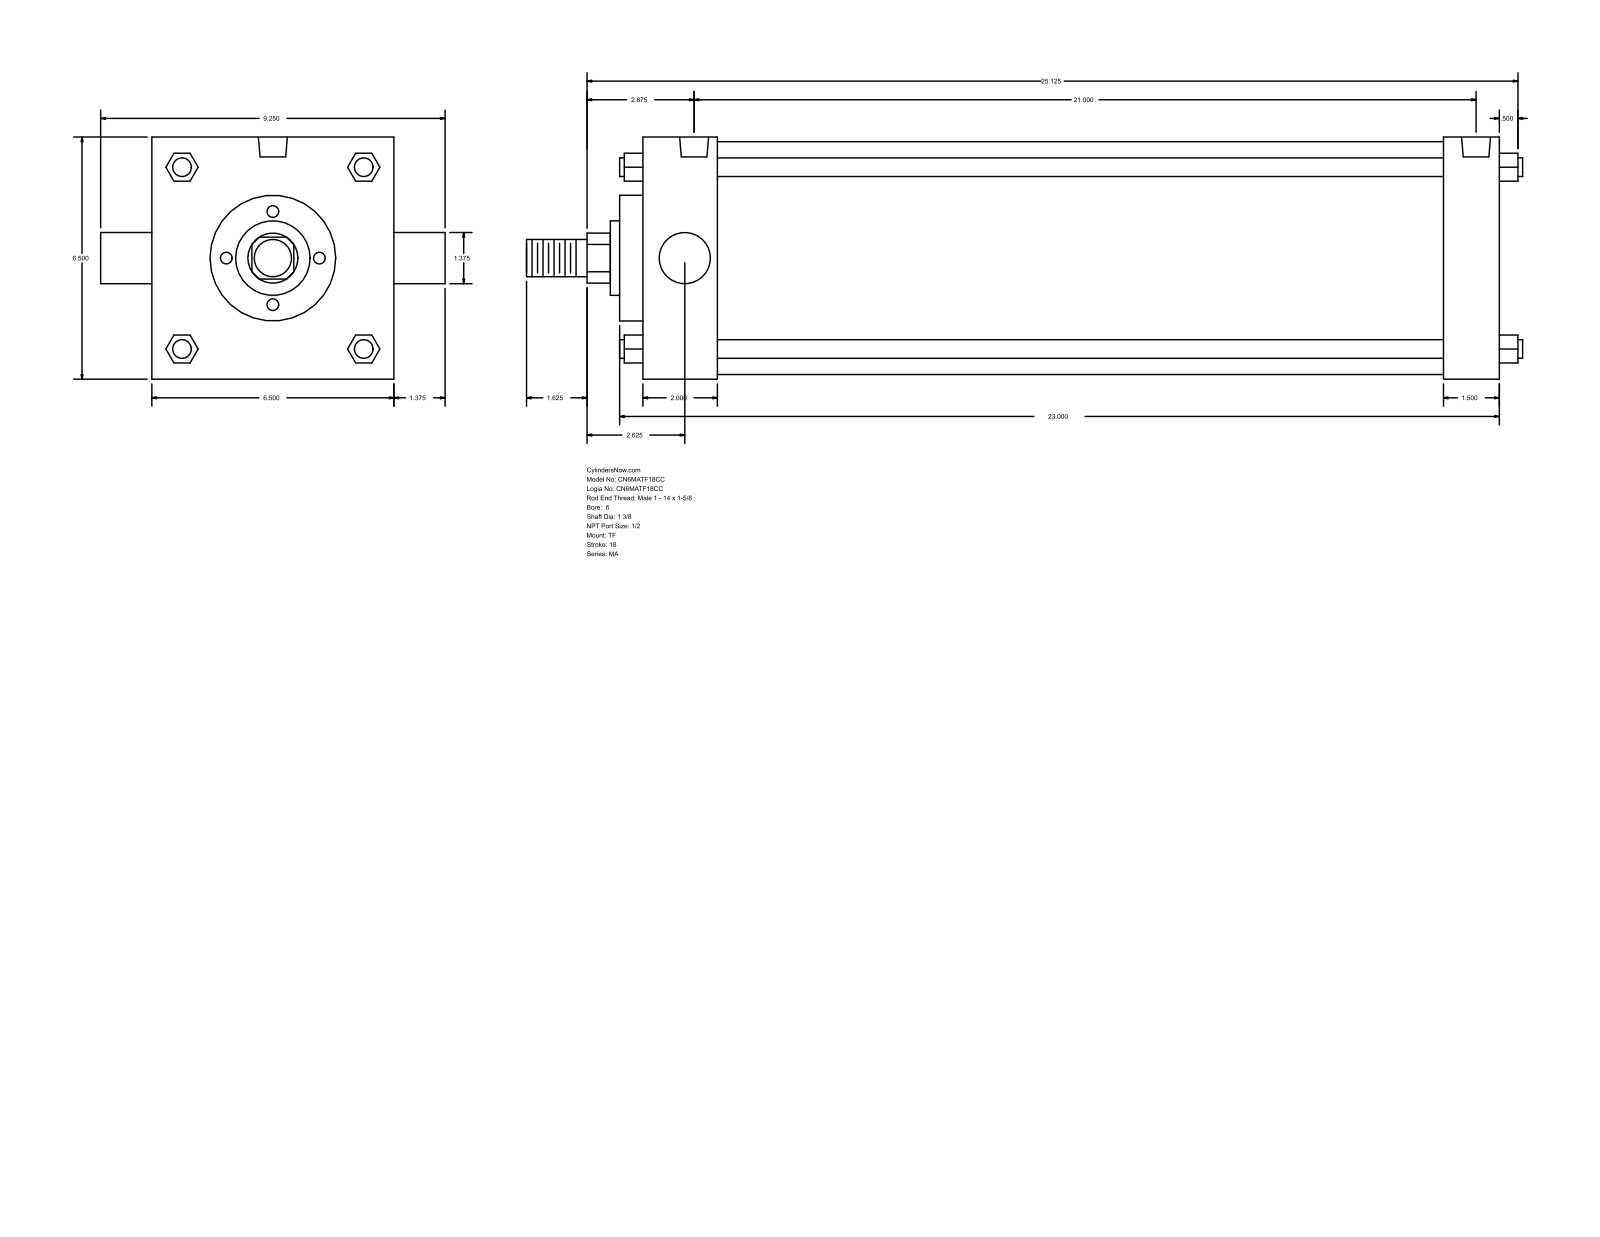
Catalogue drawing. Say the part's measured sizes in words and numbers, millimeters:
The part is named "MA_TF__0600_1.375". Its 3-D file was written by "GSSL Pune (CONFIG_CONTROL_DESIGN)". It is 0 solids with 122 faces: 93 planar, 29 cylindrical and 0 other. Overall it measures 679.45 by 234.95 by 165.1 millimeters. Round holes: 3 of diameter 17.46, 2 of diameter 19.77. Round bosses or shafts: 4 of diameter 12.7, 2 of diameter 34.92, 1 of diameter 158.75, 1 of diameter 85.72, 1 of diameter 50.8, 1 of diameter 25.4. Partial cylindrical surfaces (rounded edges, fillets, slot ends): 1 of radius 17.06. The main face-to-face distances are 165.1, 587.38, 38.1, 50.8, 536.58, 549.28, 498.48, 66.67, 15.87, 565.15. The hole center spacings are 3.18, 533.39, 536.57.
